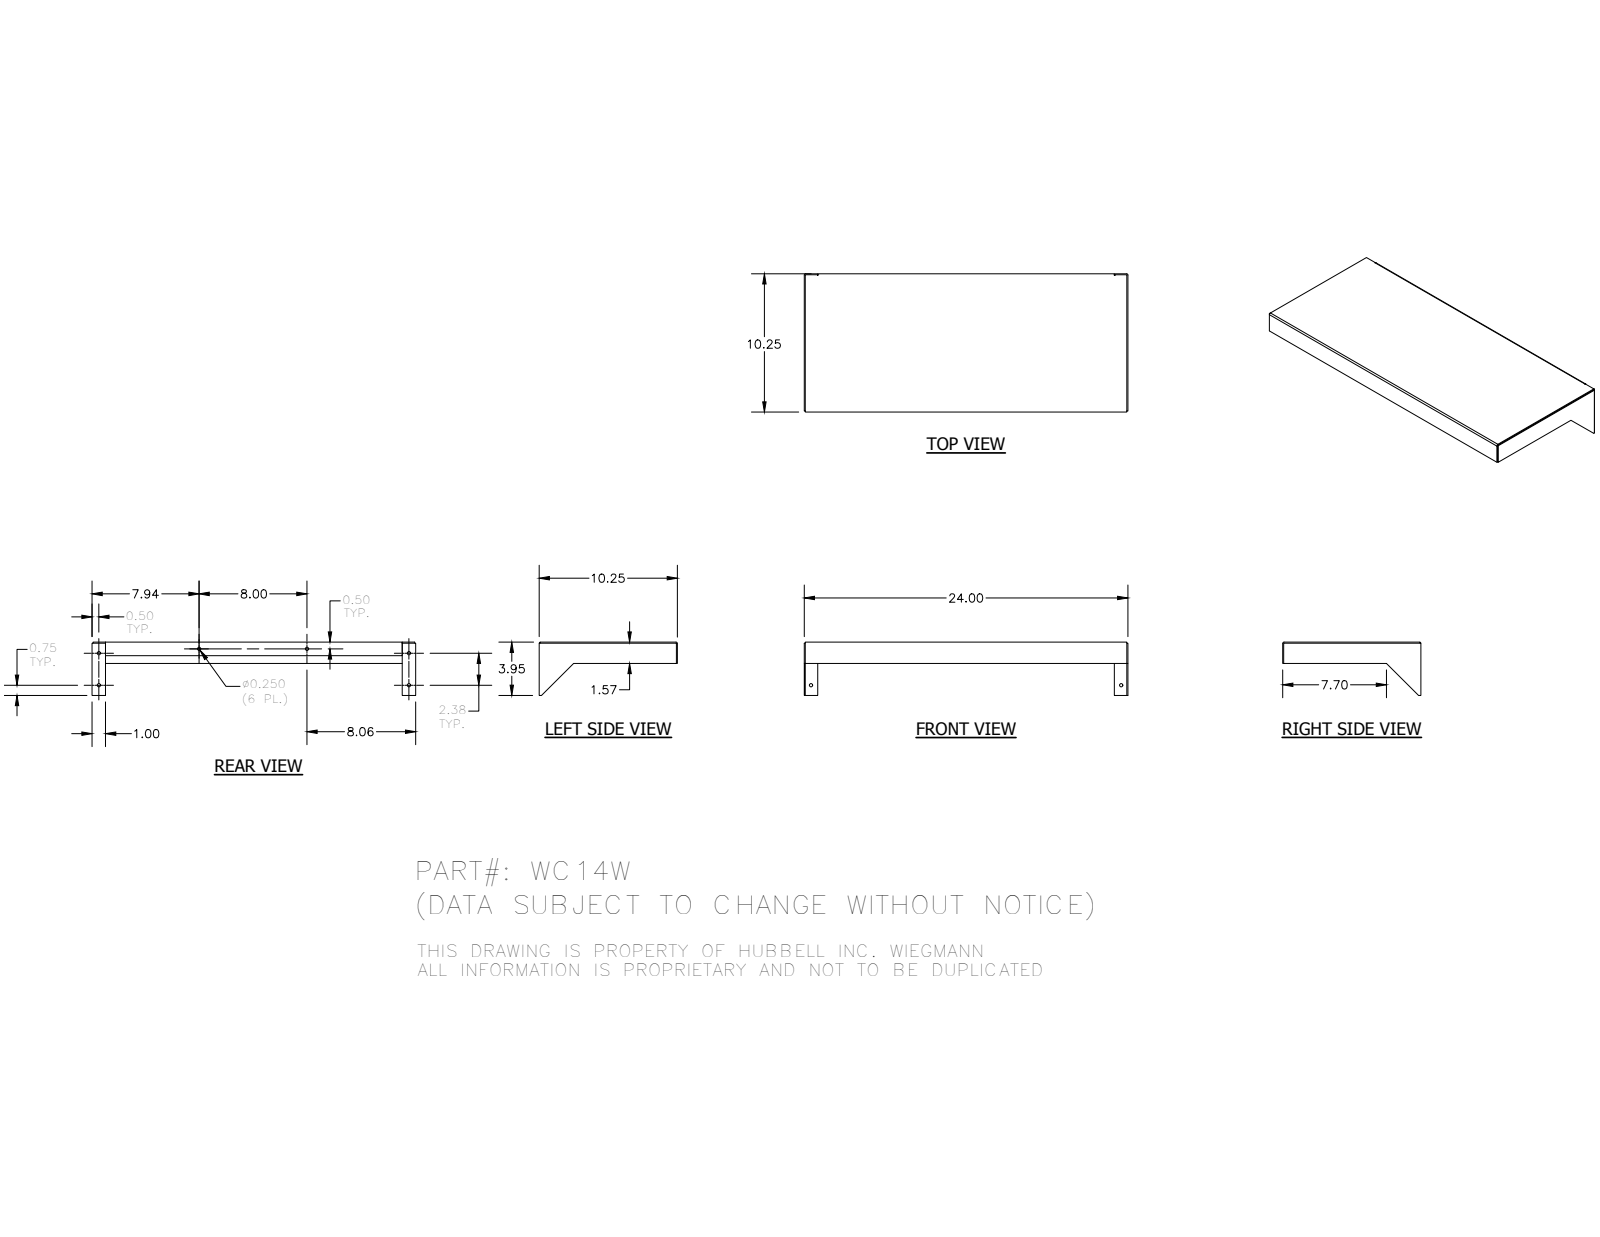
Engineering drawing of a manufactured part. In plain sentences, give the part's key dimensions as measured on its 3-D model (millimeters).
The part is named "WC14WBKP; WC14WRS; WC14WLS; WC14W". Its 3-D file was written by "Autodesk Inventor 2016 (AUTOMOTIVE_DESIGN)". It is 3 solids with 68 faces: 54 planar, 14 cylindrical and 0 other. Overall it measures 609.6 by 260.35 by 100.31 millimeters. Its volume is 415 709 cubic millimeters and its surface area 448 773 square millimeters. Round holes: 6 of diameter 6.35. Partial cylindrical surfaces (rounded edges, fillets, slot ends): 4 of radius 0.79, 4 of radius 2.67. The main face-to-face distances are 1.88, 258.47, 607.72, 256.59, 260.35, 605.84, 609.6, 39.98, 38.1, 25.4. The hole center spacings are 60.33, 584.2, 587.31, 189.1, 192.26, 200.98, 203.2, 203.95.
